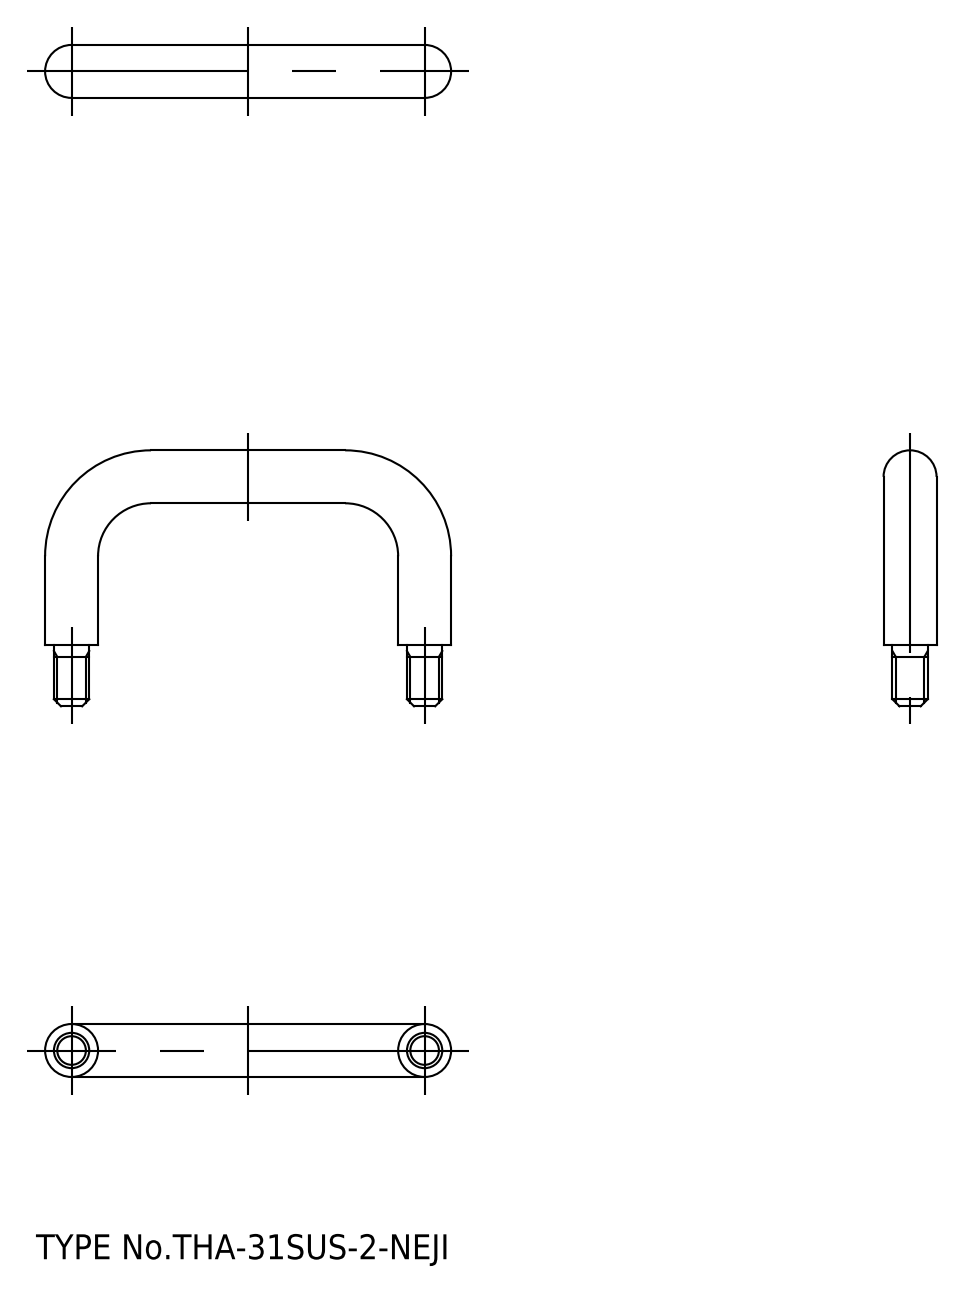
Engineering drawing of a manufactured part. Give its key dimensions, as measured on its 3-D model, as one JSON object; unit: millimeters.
{"step_written_by": "spGate 17.5.2 (AUTOMOTIVE_DESIGN)", "units": "millimeters", "bodies": {"solids": 1, "faces": 22, "planar": 4, "cylindrical": 10, "other": 8}, "overall_size": [46, 29, 6], "volume_mm3": 2161, "surface_area_mm2": 1550, "round_bosses_or_shafts": [[6, 3], [4, 2]], "face_to_face_distances": [7]}
